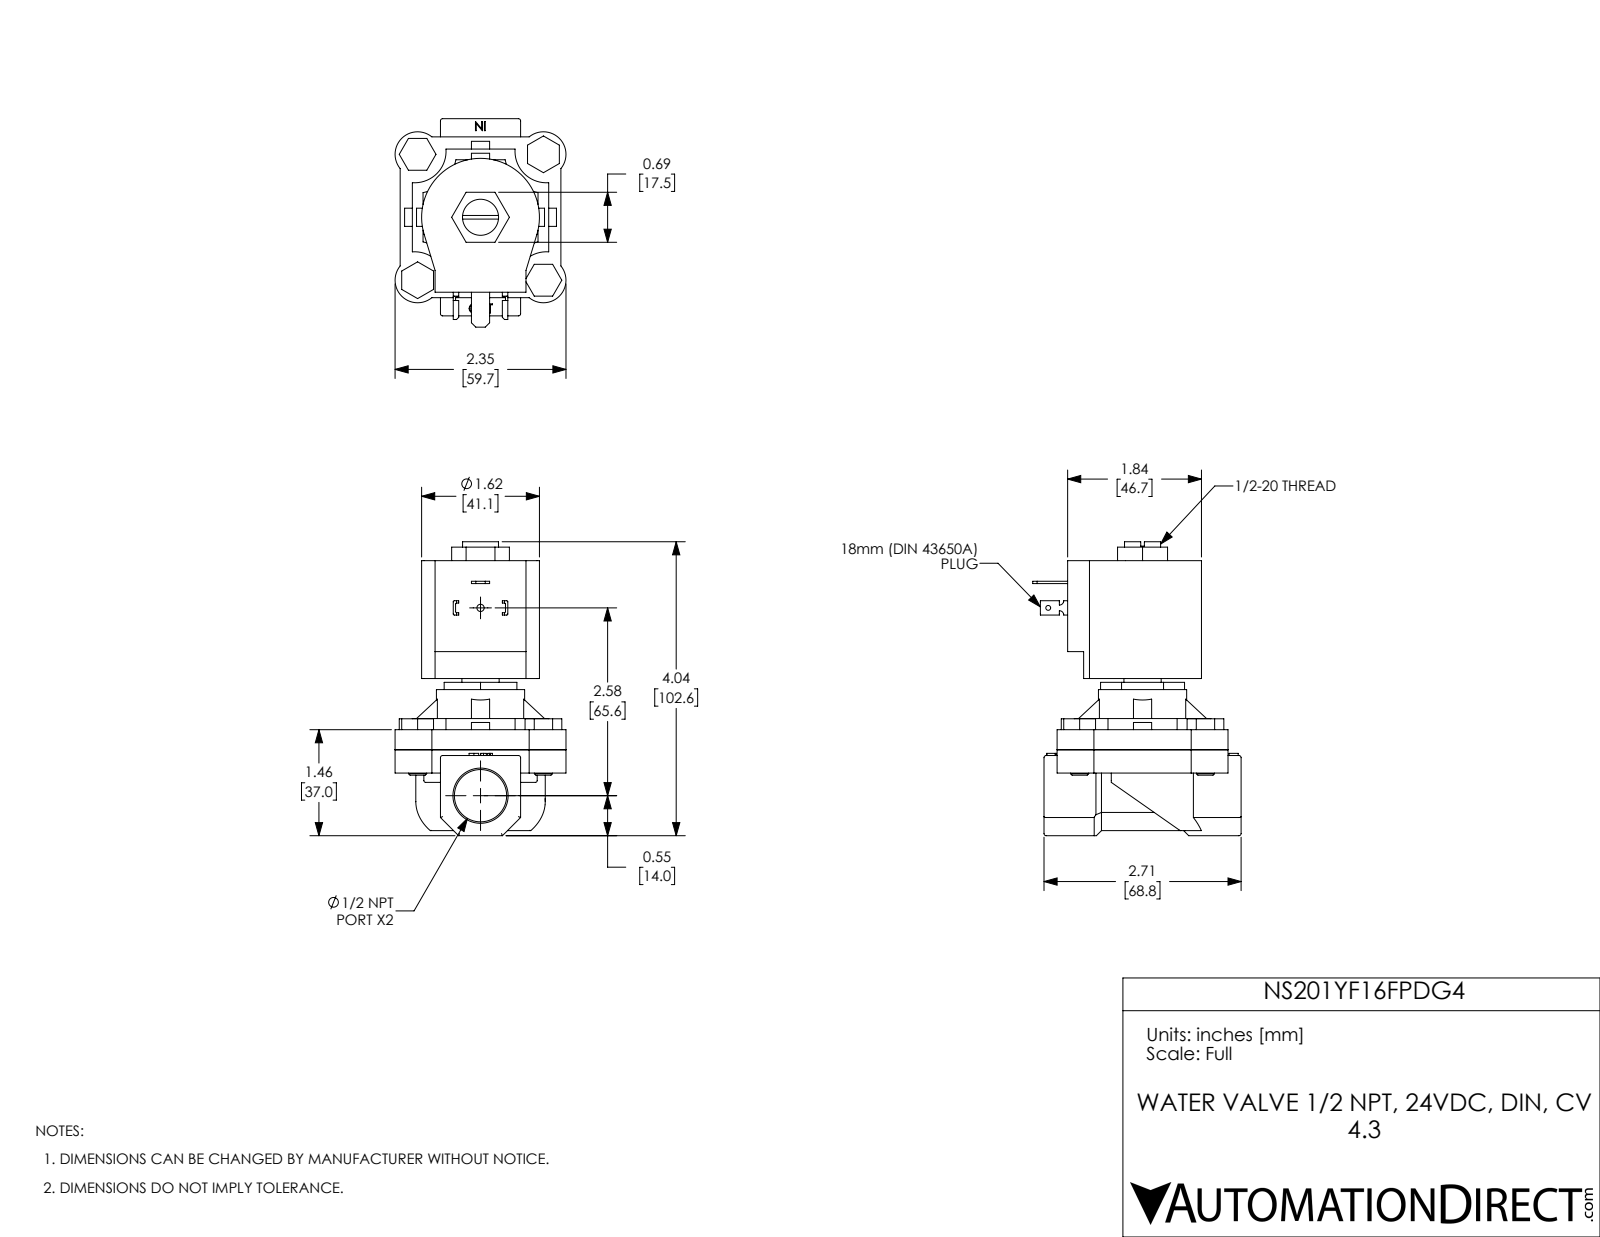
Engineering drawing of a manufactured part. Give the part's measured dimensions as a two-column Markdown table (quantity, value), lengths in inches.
| quantity | value |
| --- | --- |
| part name | NS201YF16FPDG4 |
| STEP written by | SolidWorks 2017 (AUTOMOTIVE_DESIGN) |
| units | inches |
| bodies | 11 solids, 385 faces (239 planar, 113 cylindrical, 33 other) |
| overall size | 4.04 × 2.865 × 2.35 |
| volume | 10.1 in³ |
| surface area | 67.71 in² |
| round holes (diameter × count) | 0.25 × 4, 0.067 × 1, 0.1 × 1, 0.496 × 1, 0.512 × 1, 0.719 × 1, 1.155 × 1 |
| round bosses / shafts (diameter × count) | 0.248 × 4, 1.213 × 1 |
| partial cylindrical surfaces (radius × count) | 0.03 × 15, 0.015 × 8, 0.31 × 4, 0.432 × 4, 0.579 × 4, 0.06 × 2, 0.81 × 1, 0.89 × 1 |
| main face-to-face distances | 0.276, 2.599, 2.323, 0.32, 0.596, 2.919, 0.554, 1.656, 0.25, 2.46 |
| hole center spacings | 1.223, 1.73, 2.446, 2.581 |
